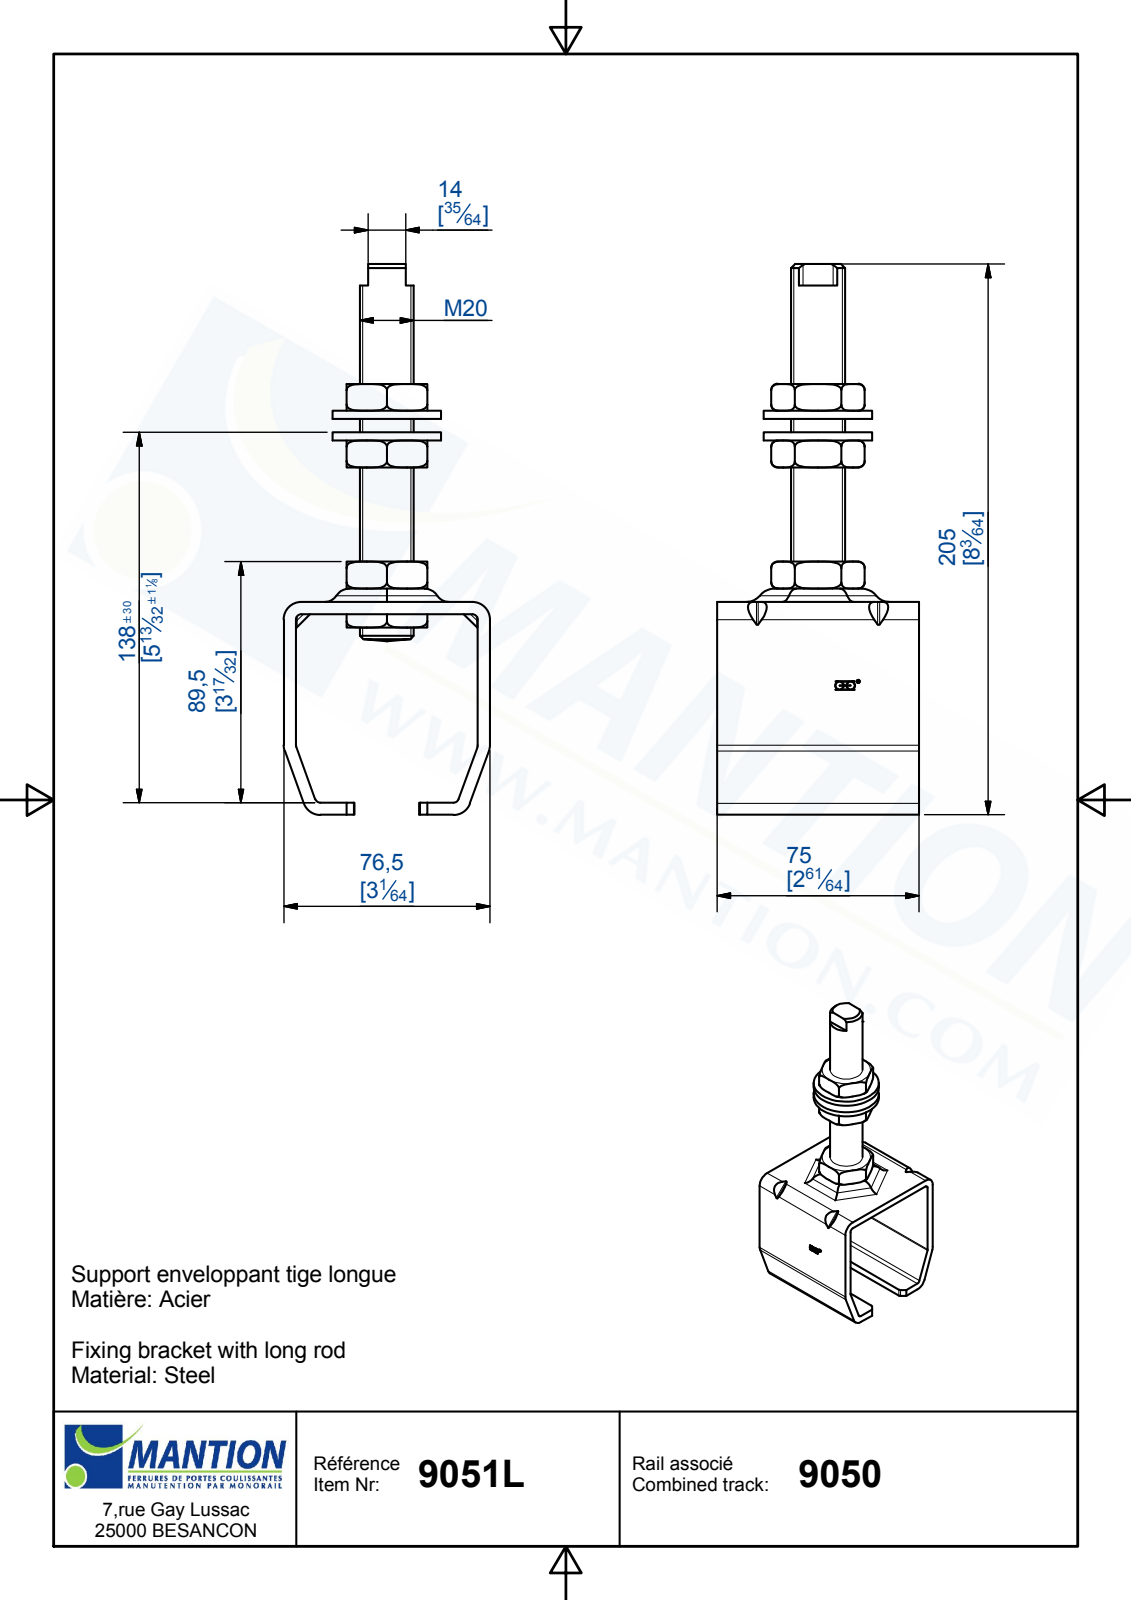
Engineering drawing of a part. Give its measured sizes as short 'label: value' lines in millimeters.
name: 9051L; 15704; 14980; 15748 (+1 more)
written by: Autodesk Inventor 2013 (AUTOMOTIVE_DESIGN)
unit: mm
bodies: 8 solids, 298 faces (152 planar, 70 cylindrical, 76 other)
size: 204.5 × 77 × 75
volume: 153 895 mm³; area: 64 934 mm²
holes: 1× ⌀1.25, 1× ⌀17.29, 1× ⌀20.1, 1× ⌀21
bosses: 2× ⌀2.9, 1× ⌀40.3, 1× ⌀20, 1× ⌀1.15
rounds: 6× R1, 6× R2, 6× R5, 6× R5.5, 6× R6.5, 6× R9.5, 4× R1.5, 2× R0.5
face distances: 4.5, 72.5, 68, 74.5, 77, 5, 8, 30, 3, 75
